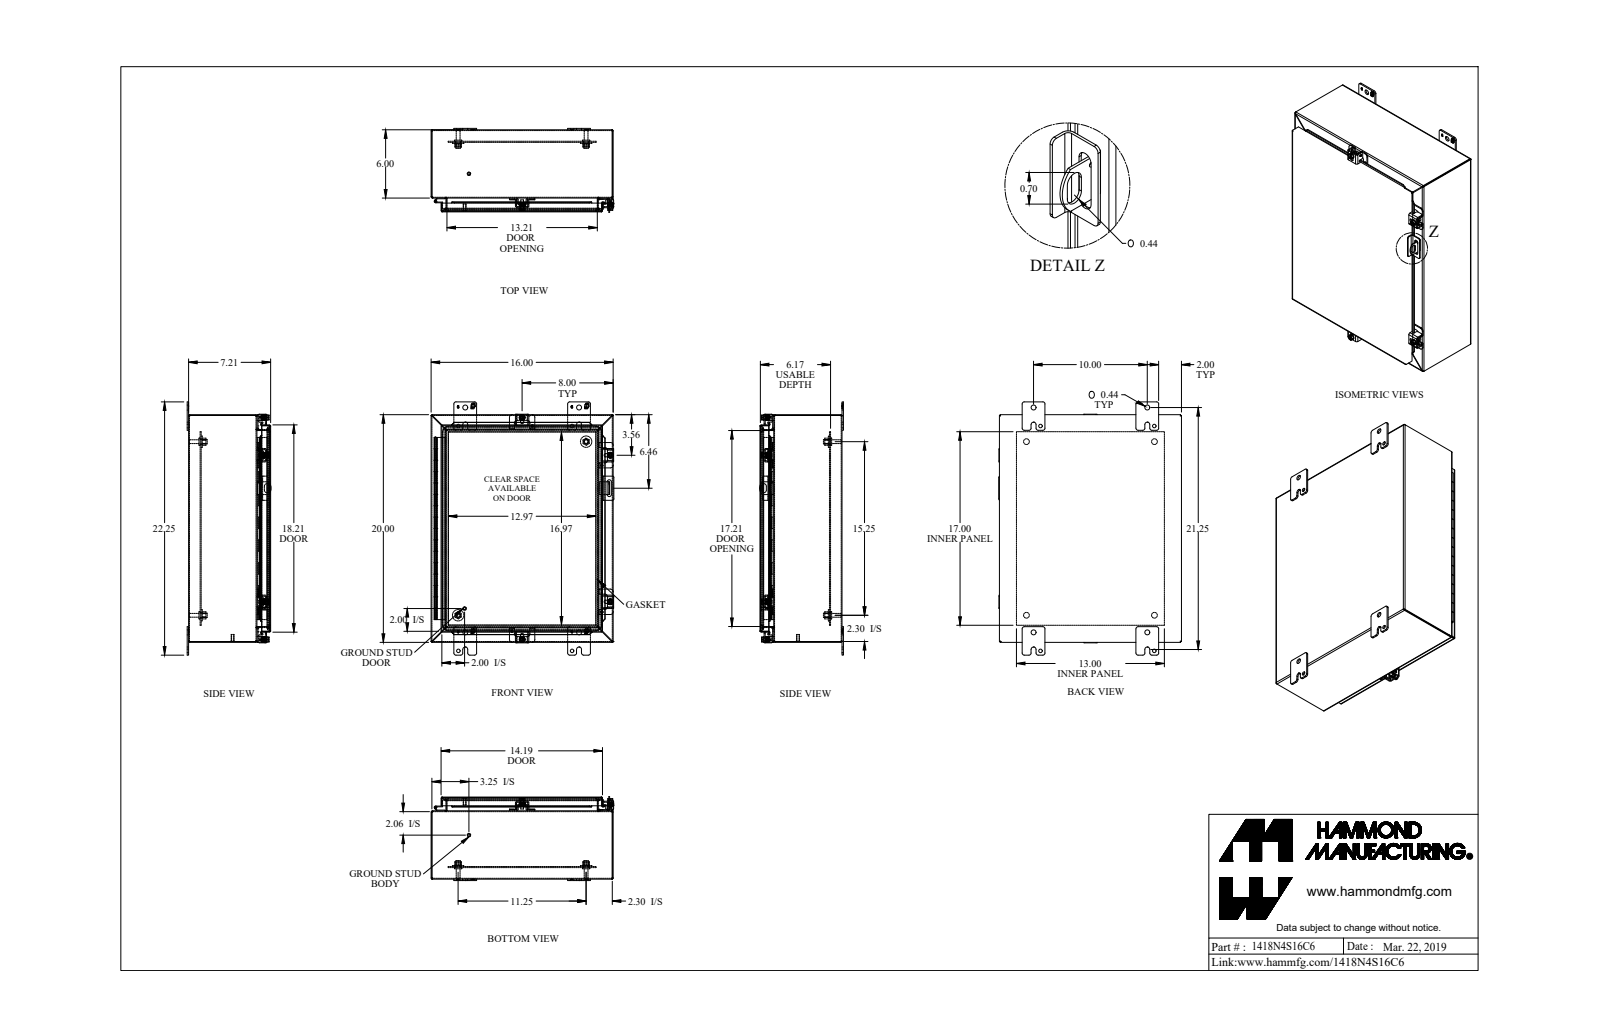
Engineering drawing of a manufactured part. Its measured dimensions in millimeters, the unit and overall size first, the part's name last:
Units: millimetres
Overall size (bounding box): 565.2 × 408 × 187.3
Round holes (diameter × count): ⌀5.4 ×4, ⌀6.7 ×4, ⌀8 ×4, ⌀9.5 ×4, ⌀11.1 ×4, ⌀12.7 ×4, ⌀7.8 ×2, ⌀11.3 ×2, ⌀2.8 ×1, ⌀3.2 ×1
Round bosses / shafts (diameter × count): ⌀16.5 ×4, ⌀12.7 ×4, ⌀9.9 ×4, ⌀9.5 ×4, ⌀8.4 ×4, ⌀6.2 ×4, ⌀25.4 ×2, ⌀8 ×2
Partial cylindrical surfaces — rounded edges, fillets, slot ends (radius × count): R4.8 ×26, R0.9 ×24, R2.7 ×24, R1.2 ×21, R3.6 ×21, R6.4 ×20, R3.2 ×10, R1.1 ×8
Main face-to-face distances: 1.8, 1.8, 179.5, 181.3, 181.3, 23.8, 183.1, 25.6, 404.6, 2.4
Hole centre spacings: 463.9, 152.7, 254, 61.8, 77.9, 280.4, 285.8, 387.4
Volume: 1 993 000 mm³ · Surface area: 2 075 000 mm²
Bodies: 39 solids, 1329 faces (728 planar, 467 cylindrical, 134 other)
Part name (STEP PRODUCT): 1418N4S16C6_Default
STEP written by: SolidWorks 2019 (CONFIG_CONTROL_DESIGN)
